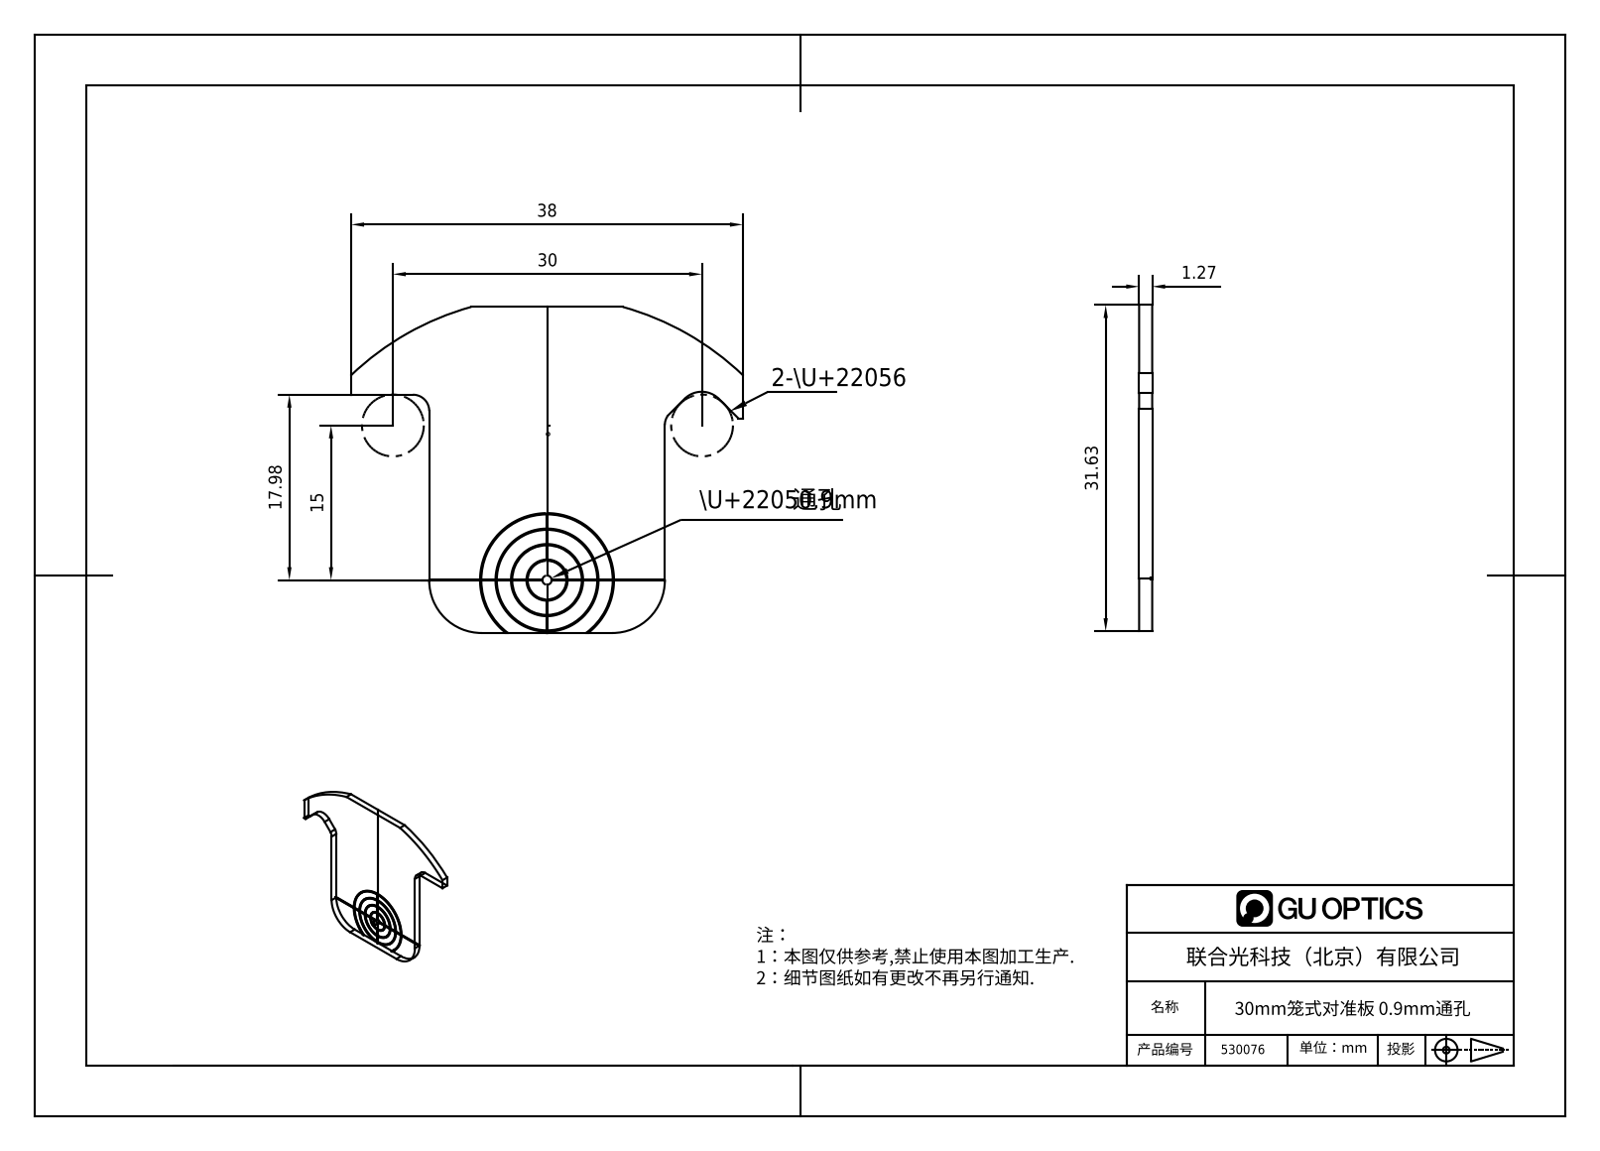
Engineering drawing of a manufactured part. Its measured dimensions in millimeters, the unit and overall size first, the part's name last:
Units: millimetres
Overall size (bounding box): 38 × 31.63 × 1.27
Round holes (diameter × count): ⌀0.89 ×1, ⌀4 ×1, ⌀7 ×1, ⌀10 ×1
Round bosses / shafts (diameter × count): ⌀9.75 ×1, ⌀6.75 ×1, ⌀3.75 ×1
Partial cylindrical surfaces — rounded edges, fillets, slot ends (radius × count): R1.57 ×2, R5.08 ×2, R2.35 ×1, R6.37 ×1, R6.5 ×1, R27.5 ×1
Main face-to-face distances: 1.27, 22.86, 1.14, 31.63, 7.57, 30.43, 23.11, 8.52, 18.96, 11.39
Bodies: 0 solids, 102 faces (61 planar, 41 cylindrical, 0 other)
Part name (STEP PRODUCT): 1.9.1.2，ZAB-30-0.9，30mm笼式准直板，0.9mm通孔，A
STEP written by: SolidWorks 2018 (AUTOMOTIVE_DESIGN)
